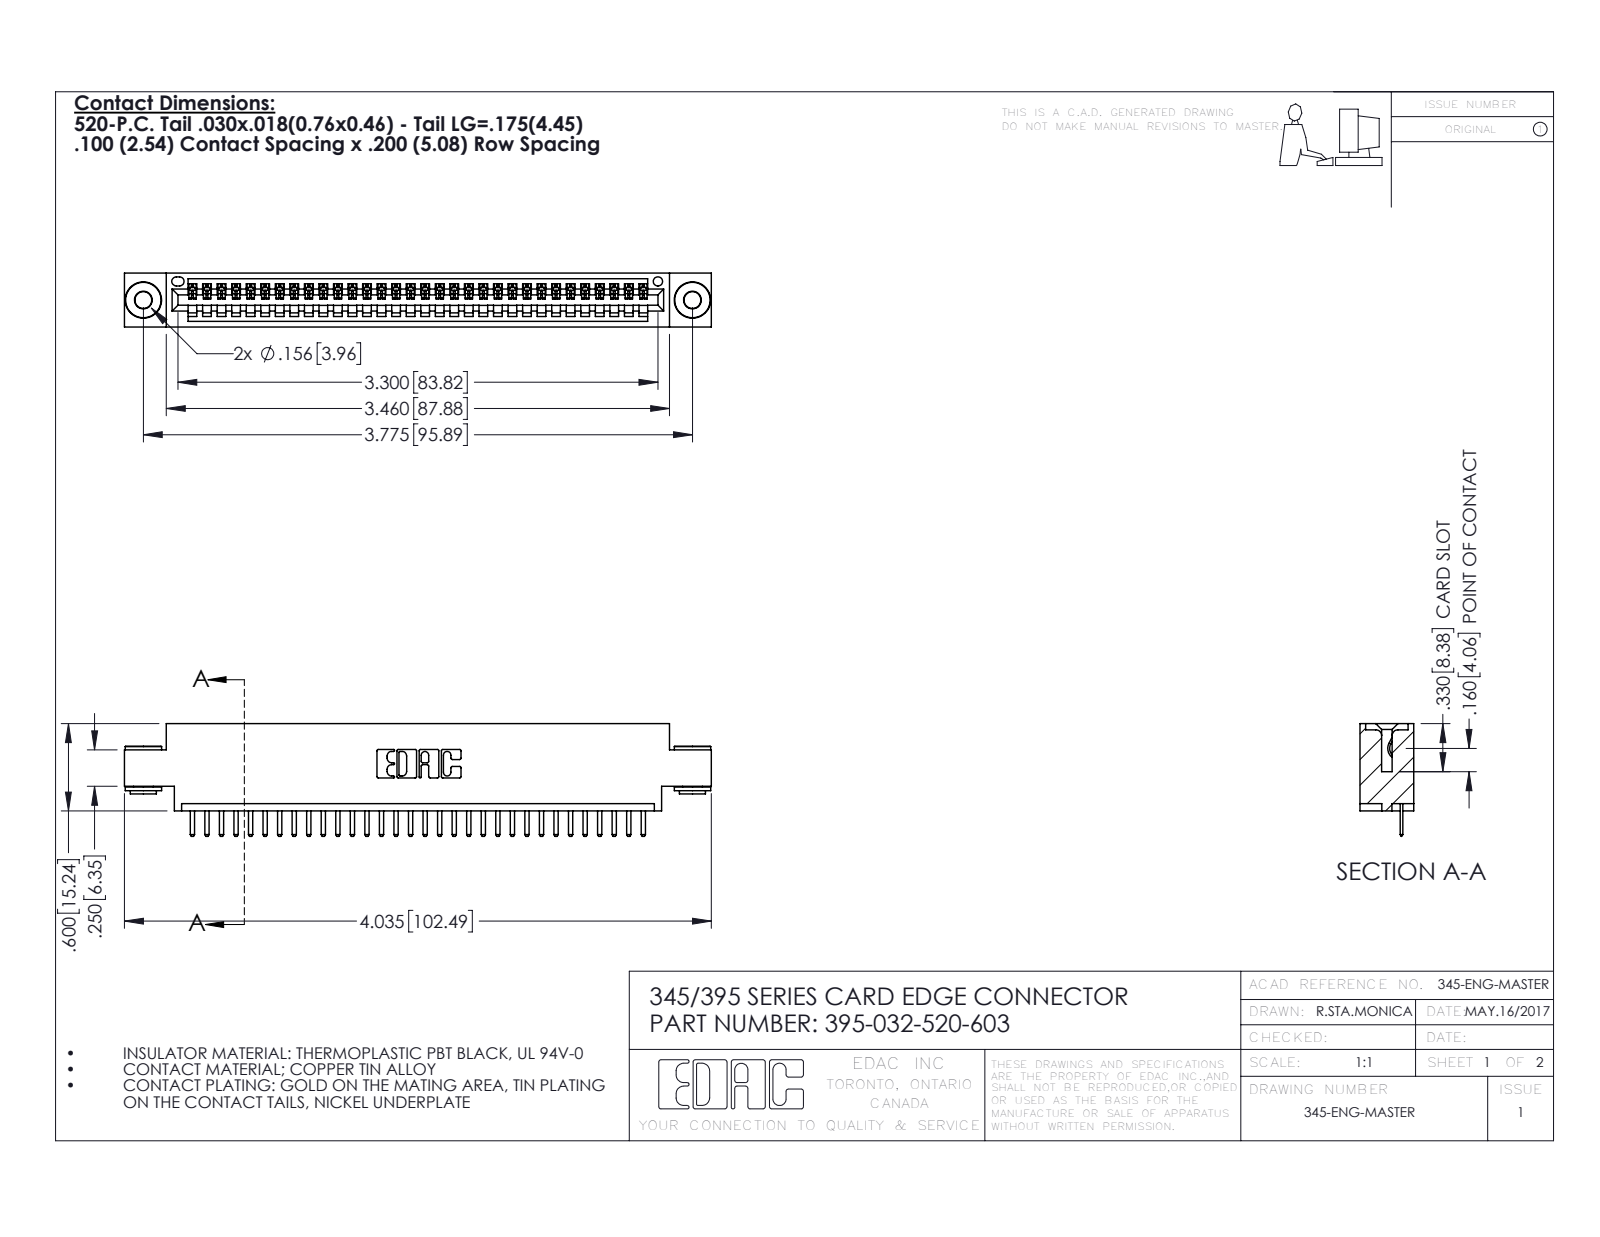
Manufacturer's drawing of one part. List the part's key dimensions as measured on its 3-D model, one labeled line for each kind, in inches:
Part name (STEP PRODUCT): 345-250-002_345-250-002-102; 395-032-520-603; 345 Part_0.170 Offset - 0.156 Dia-TH; 345-292-001_345-293-120
STEP written by: SolidWorks 2016 (CONFIG_CONTROL_DESIGN)
Units: inches
Bodies: 35 solids, 2152 faces (1438 planar, 706 cylindrical, 8 other)
Overall size (bounding box): 4.035 × 0.775 × 0.37
Volume: 0.578 in³ · Surface area: 19.35 in²
Round holes (diameter × count): ⌀0.116 ×2, ⌀0.156 ×2, ⌀0.064 ×1
Round bosses / shafts (diameter × count): ⌀0.25 ×2, ⌀0.18 ×2, ⌀0.136 ×2
Partial cylindrical surfaces — rounded edges, fillets, slot ends (radius × count): R0.01 ×66, R0.006 ×64, R0.01 ×22, R0.007 ×6, R0.031 ×6, R0.026 ×3, R0.031 ×2, R0.04 ×2
Main face-to-face distances: 0.072, 0.298, 0.37, 0.2, 0.098, 0.272, 0.025, 0.225, 0.175, 0.072
Hole centre spacings: 0.27, 3.54, 3.775
